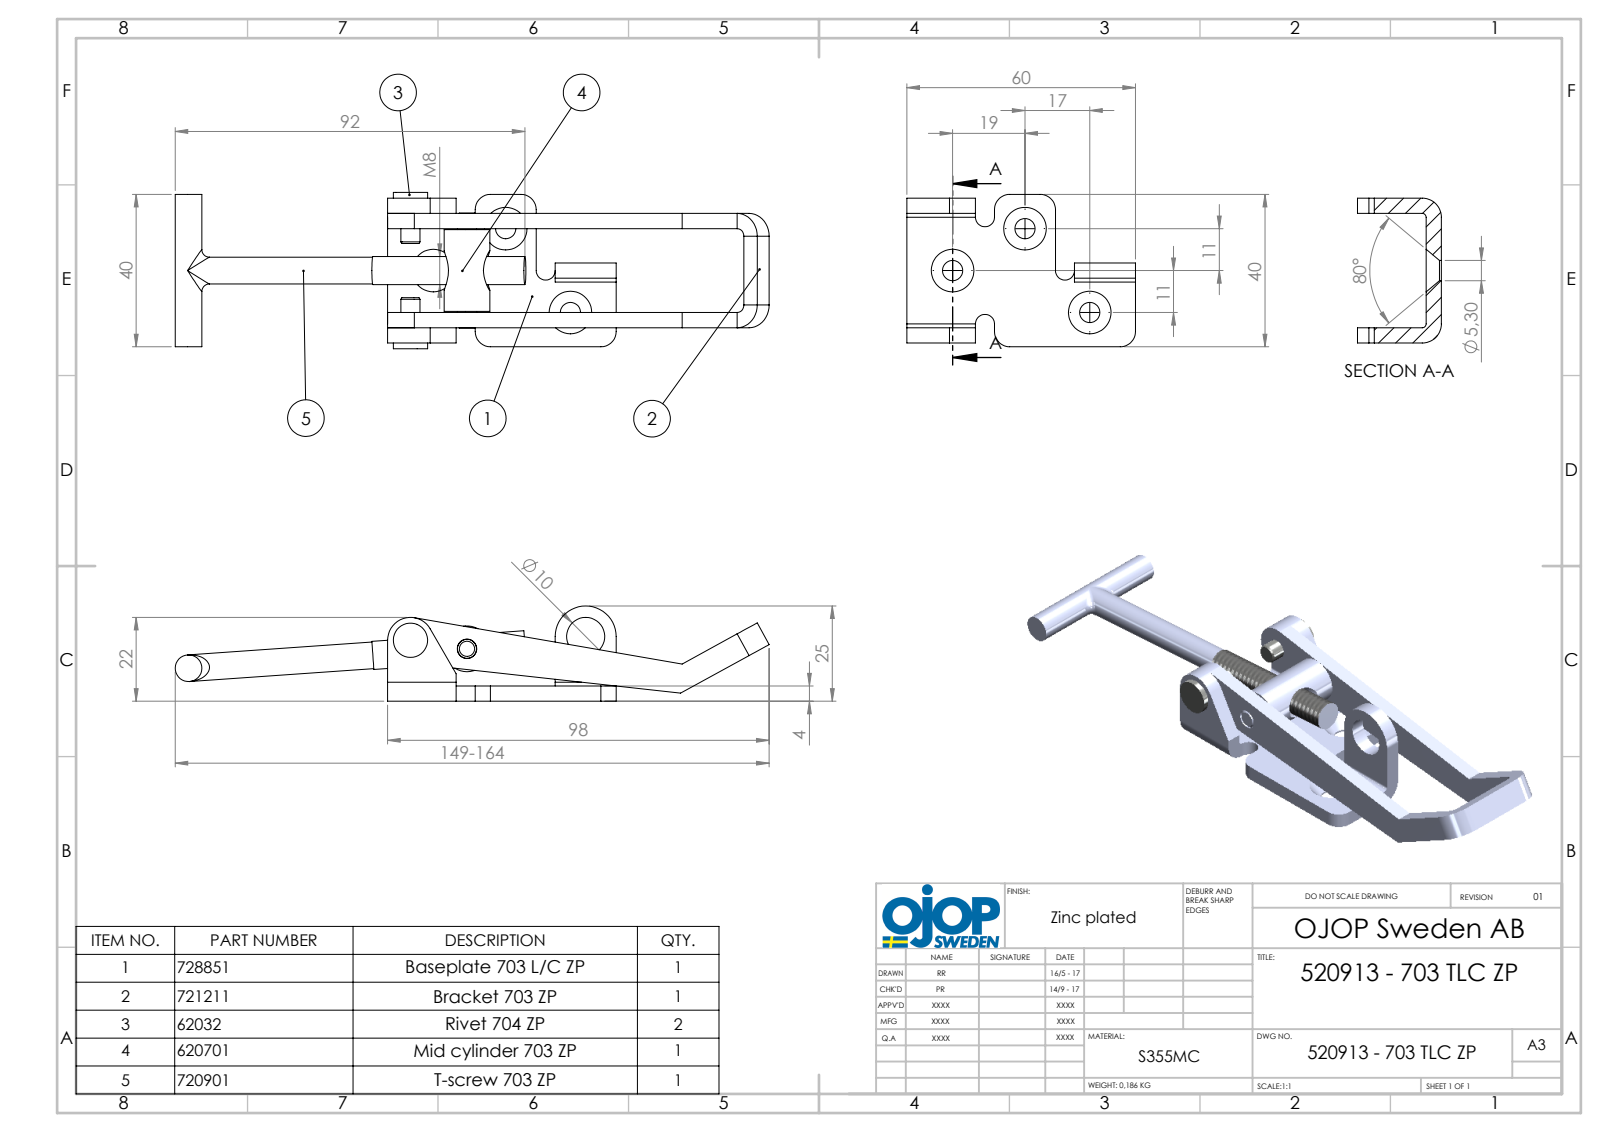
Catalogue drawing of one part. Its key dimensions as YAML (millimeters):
part_name: "520913; 704 - Rivet Gradin; 703 - T-skruv; 703 - Rulle (+2 more)"
step_written_by: "SolidWorks 2015 (AUTOMOTIVE_DESIGN)"
units: millimeters
bodies: {solids: 6, faces: 157, planar: 66, cylindrical: 71, other: 20}
overall_size: [152.41, 41, 25]
volume: 24484
surface_area: 17225
round_holes:
  - {diameter: 5.3, count: 3}
  - {diameter: 5.1, count: 2}
  - {diameter: 7.2, count: 1}
  - {diameter: 7.7, count: 1}
  - {diameter: 10, count: 1}
round_bosses_or_shafts:
  - {diameter: 7, count: 3}
  - {diameter: 5, count: 2}
  - {diameter: 12, count: 1}
  - {diameter: 9, count: 1}
  - {diameter: 7.4, count: 1}
partial_cylinders:
  - {radius: 4, count: 4}
  - {radius: 1, count: 3}
  - {radius: 2.5, count: 3}
  - {radius: 5, count: 3}
  - {radius: 6, count: 3}
  - {radius: 2, count: 2}
  - {radius: 8, count: 1}
face_to_face_distances: [4, 26, 30, 22, 17, 13, 9, 21, 8, 34]
hole_center_spacings: [15.01, 21.95, 27.8, 31.31, 37.64, 46.01]
